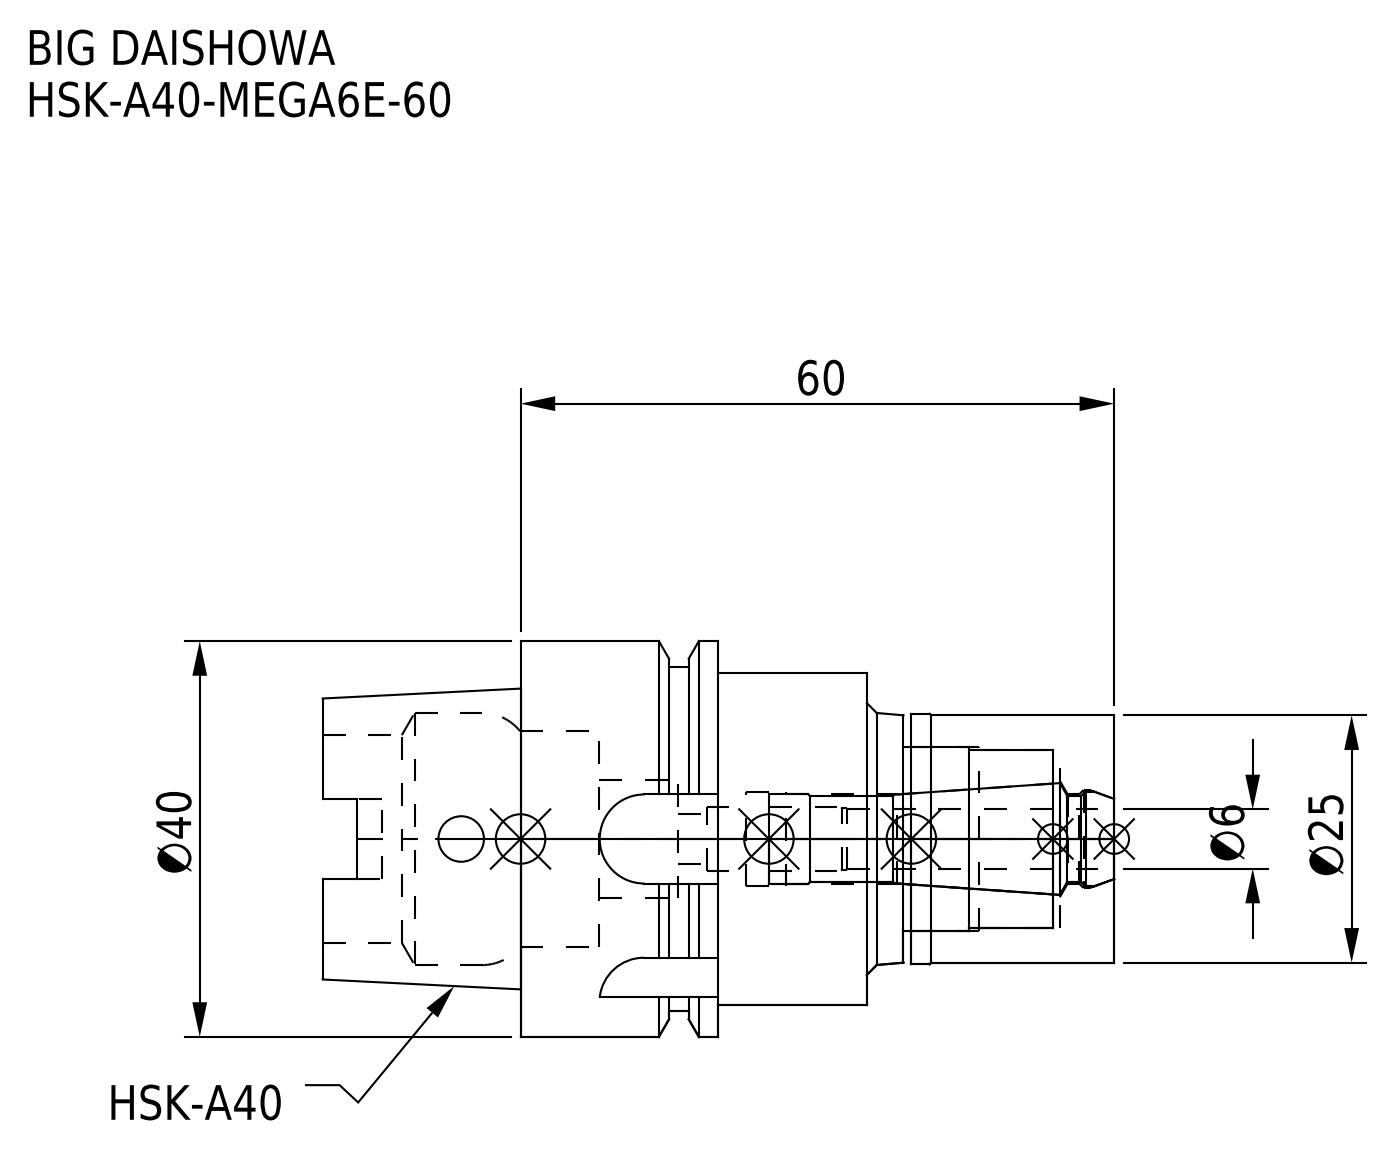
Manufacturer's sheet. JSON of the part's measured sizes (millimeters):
{"part_name": "HSK-A40-MEGA6E-60-060.stp; DXF_TEMP_ASSY_ASM_4_ASM.stp; HSK-A40-MEGA6E-60-060-FreeParts; HSK-A40-MEGA6E-60_1.stp (+3 more)", "step_written_by": "SolidWorks 2019 (CONFIG_CONTROL_DESIGN)", "units": "millimeters", "bodies": {"solids": 2, "faces": 130, "planar": 46, "cylindrical": 56, "other": 28}, "overall_size": [80, 40, 40], "volume_mm3": 46909, "surface_area_mm2": 16704, "round_holes": [[4.6, 1], [5, 1], [6.4, 1], [9, 1], [9.6, 1], [9.9, 1], [12, 1], [18, 1], [18.5, 1], [21, 1], [21.8, 1], [25.5, 1]], "round_bosses_or_shafts": [[40, 1], [34.8, 1], [33.6, 1], [25.3, 1], [25, 1]], "partial_cylinders_radius": [[1.88, 4], [4.5, 4]], "face_to_face_distances": [20, 15, 40, 60, 19.5, 35, 39.5, 25, 52.05, 27.05]}
